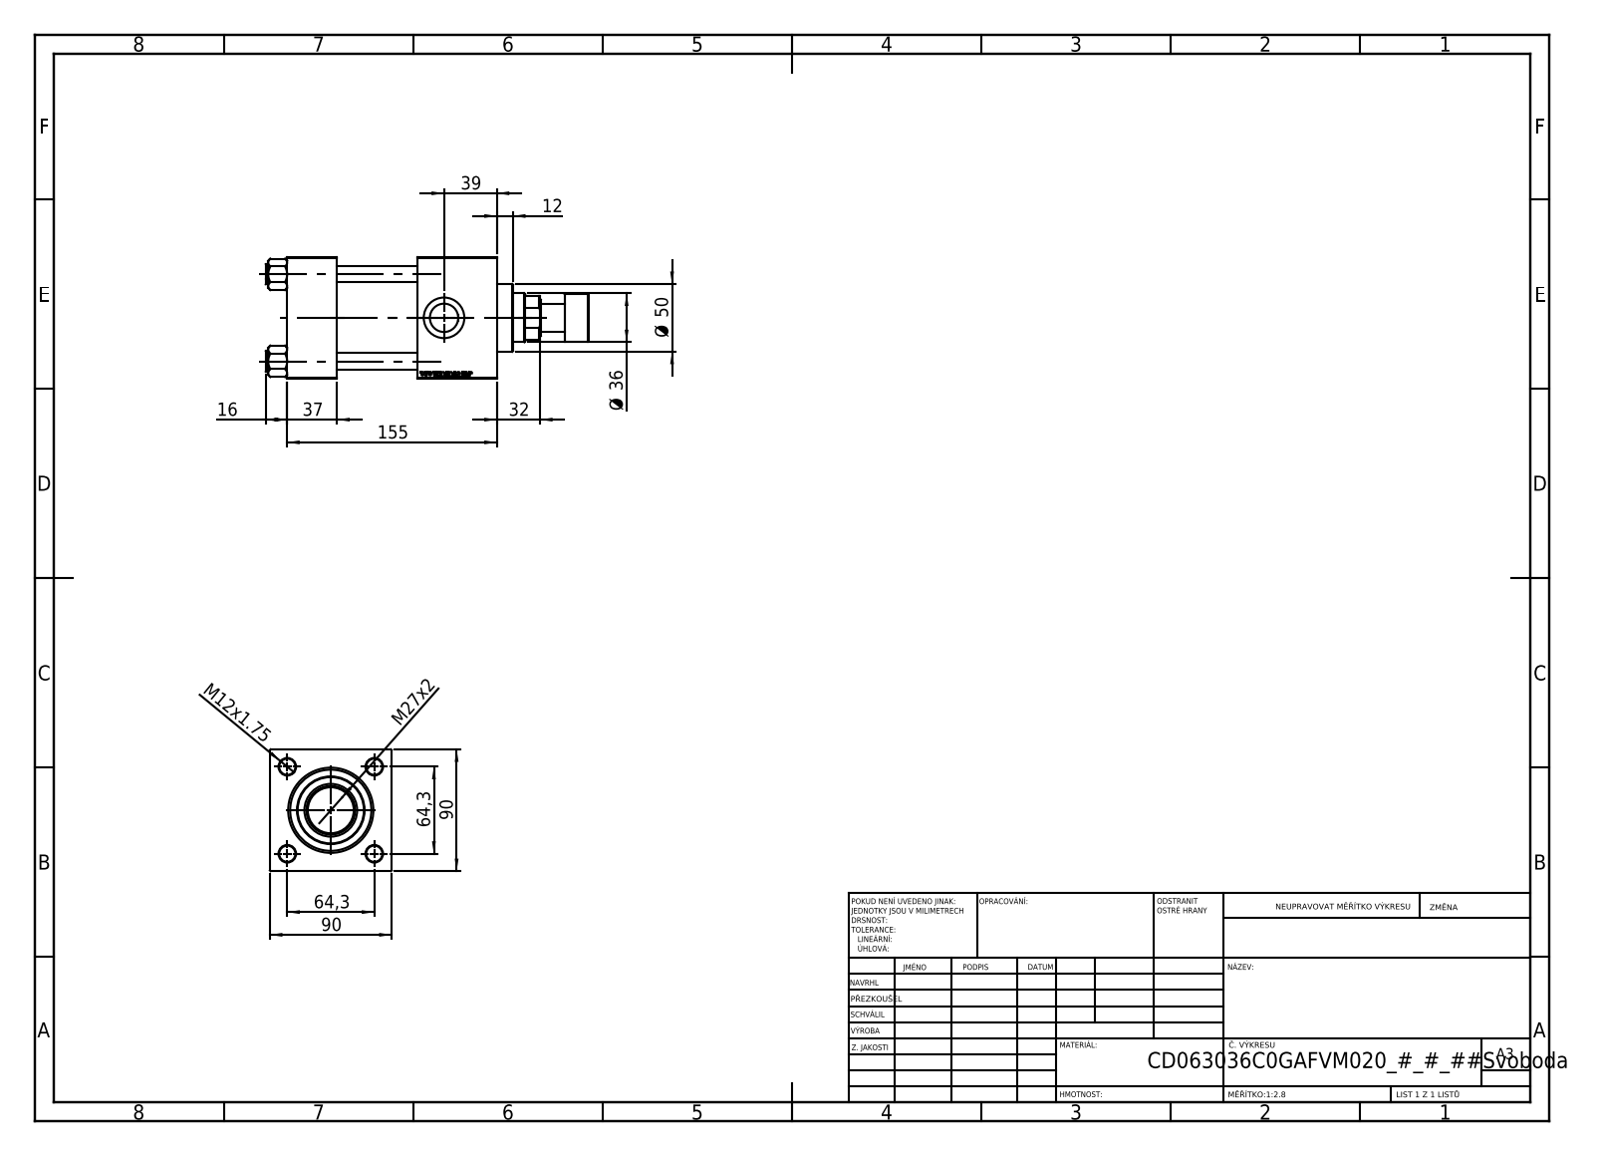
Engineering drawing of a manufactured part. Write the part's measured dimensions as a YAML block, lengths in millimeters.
part_name: "V215CD_VCP_C; V215CD_C_TYCINKA; V215CD_VC_C; V215CD_Body_C (+2 more)"
step_written_by: "SolidWorks 2019 (CONFIG_CONTROL_DESIGN)"
units: millimeters
bodies: {solids: 12, faces: 1163, planar: 530, cylindrical: 91, other: 542}
overall_size: [239, 90, 90]
volume: 991498
surface_area: 189805
round_holes:
  - {diameter: 12, count: 4}
  - {diameter: 7, count: 2}
  - {diameter: 20.96, count: 2}
  - {diameter: 30, count: 2}
  - {diameter: 25.5, count: 1}
  - {diameter: 36, count: 1}
  - {diameter: 39, count: 1}
  - {diameter: 50, count: 1}
  - {diameter: 60, count: 1}
  - {diameter: 63, count: 1}
round_bosses_or_shafts:
  - {diameter: 15, count: 4}
  - {diameter: 69, count: 1}
  - {diameter: 35, count: 1}
  - {diameter: 21, count: 1}
face_to_face_distances: [90, 59, 37, 96, 155, 118, 20, 126.3, 89.3, 30.3]
hole_center_spacings: [45.47, 64.3, 90.93]
